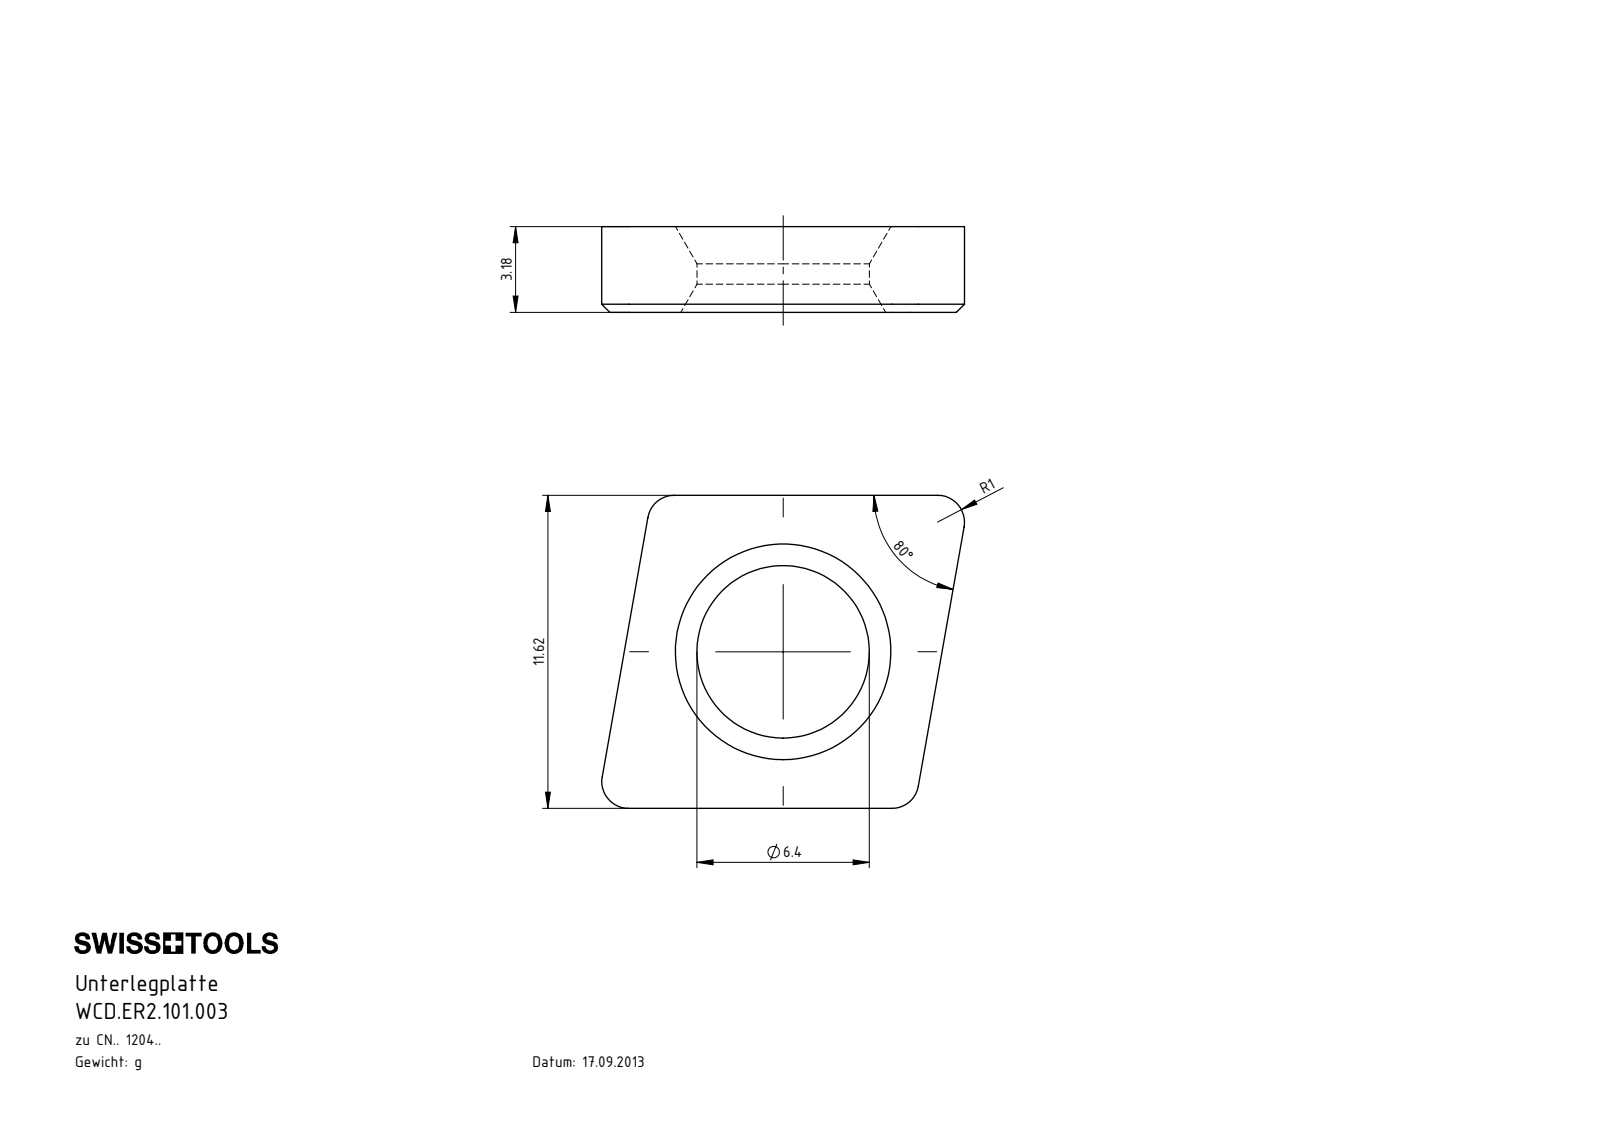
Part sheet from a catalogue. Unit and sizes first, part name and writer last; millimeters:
Units: millimetres
Overall size (bounding box): 13.46 × 11.62 × 3.18
Round holes (diameter × count): ⌀6.4 ×1
Partial cylindrical surfaces — rounded edges, fillets, slot ends (radius × count): R1 ×4
Main face-to-face distances: 3.18, 11.62
Volume: 310 mm³ · Surface area: 391 mm²
Bodies: 1 solid, 21 faces (10 planar, 5 cylindrical, 6 other)
Part name (STEP PRODUCT): WCD.ER2.101.003
STEP written by: SolidWorks 2017 (AUTOMOTIVE_DESIGN)
